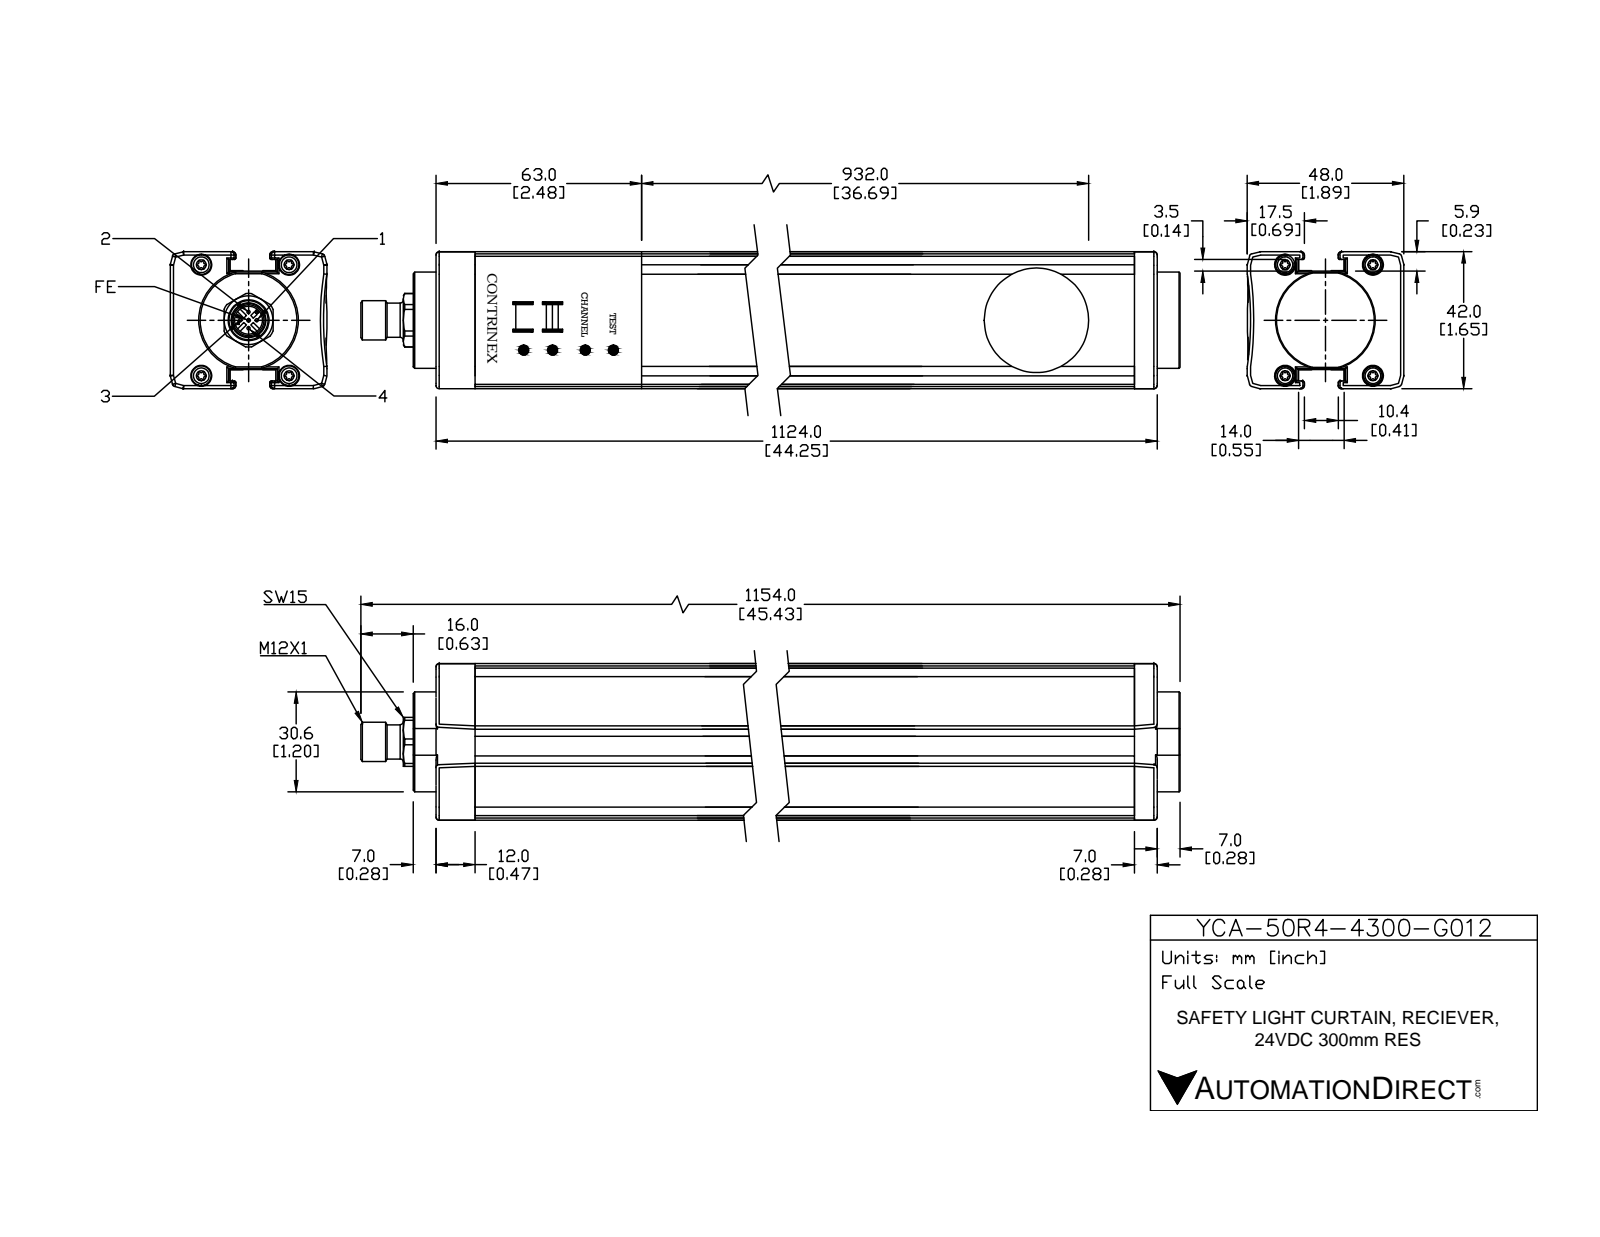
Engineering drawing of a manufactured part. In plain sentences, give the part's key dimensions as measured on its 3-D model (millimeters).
The part is named "YCA-50R4-4300-G012". Its 3-D file was written by "SolidWorks 2016 (AUTOMOTIVE_DESIGN)". It is 18 solids with 454 faces: 221 planar, 172 cylindrical and 61 other. Overall it measures 1154 by 48 by 42 millimeters. Its volume is 2 025 000 cubic millimeters and its surface area 259 577 square millimeters. Round holes: 4 of diameter 6, 1 of diameter 1, 1 of diameter 8.5, 1 of diameter 32. Round bosses or shafts: 4 of diameter 5.5, 4 of diameter 1, 1 of diameter 30.6, 1 of diameter 12, 1 of diameter 10.5. Partial cylindrical surfaces (rounded edges, fillets, slot ends): 52 of radius 1, 4 of radius 0.5, 1 of radius 8.2, 1 of radius 100. The main face-to-face distances are 42, 5.8, 36.2, 29.4, 1, 6.8, 35.2, 30.4, 14, 17.2. The hole center spacings are 21.04, 22.34, 26.9, 34, 43.35.
